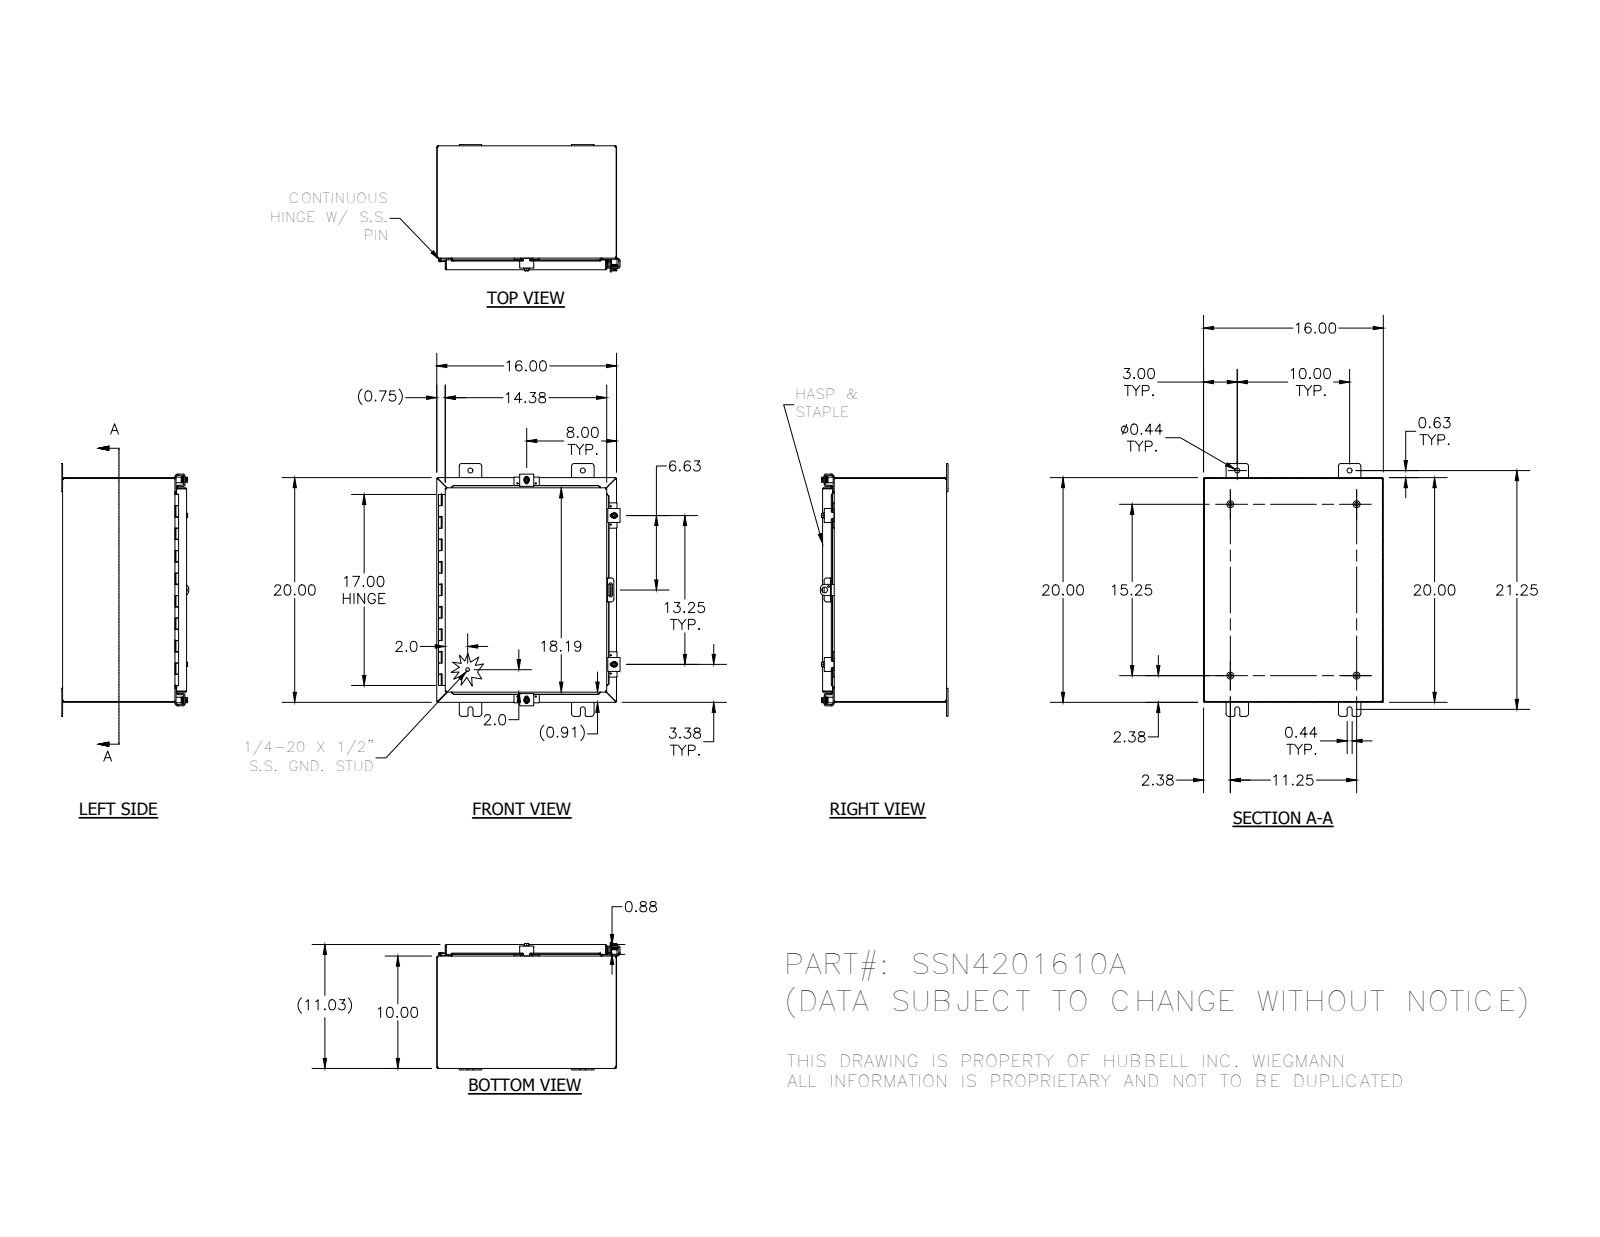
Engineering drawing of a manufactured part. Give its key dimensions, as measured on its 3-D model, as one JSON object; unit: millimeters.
{"part_name": "32874-20L; 32874-20T; SSN42016ALID; 38846 (+8 more)", "step_written_by": "SolidWorks 2014 (AUTOMOTIVE_DESIGN)", "units": "millimeters", "bodies": {"solids": 37, "faces": 1428, "planar": 575, "cylindrical": 612, "other": 241}, "overall_size": [571.5, 411.9, 288.4], "volume_mm3": 2047000, "surface_area_mm2": 2113000, "round_holes": [[2.8, 8], [5.4, 4], [7.1, 4], [7.6, 4], [11.1, 4], [3.2, 1], [4, 1], [12.7, 1]], "round_bosses_or_shafts": [[6.4, 6], [15.9, 4], [13.2, 4], [12.7, 4], [8.9, 4], [8.4, 4], [8.6, 1], [3, 1]], "partial_cylinders_radius": [[0.8, 49], [3.2, 33], [6.4, 29], [0.8, 23], [2.7, 23], [1.6, 14], [1.8, 8], [3.6, 8]], "face_to_face_distances": [1.9, 278.4, 404.5, 506.1, 276.5, 280.2, 406.4, 402.6, 252.1, 26.2], "hole_center_spacings": [22.3, 490.4, 336.6, 22.3, 41.3, 41.3, 106.4, 110.3]}
